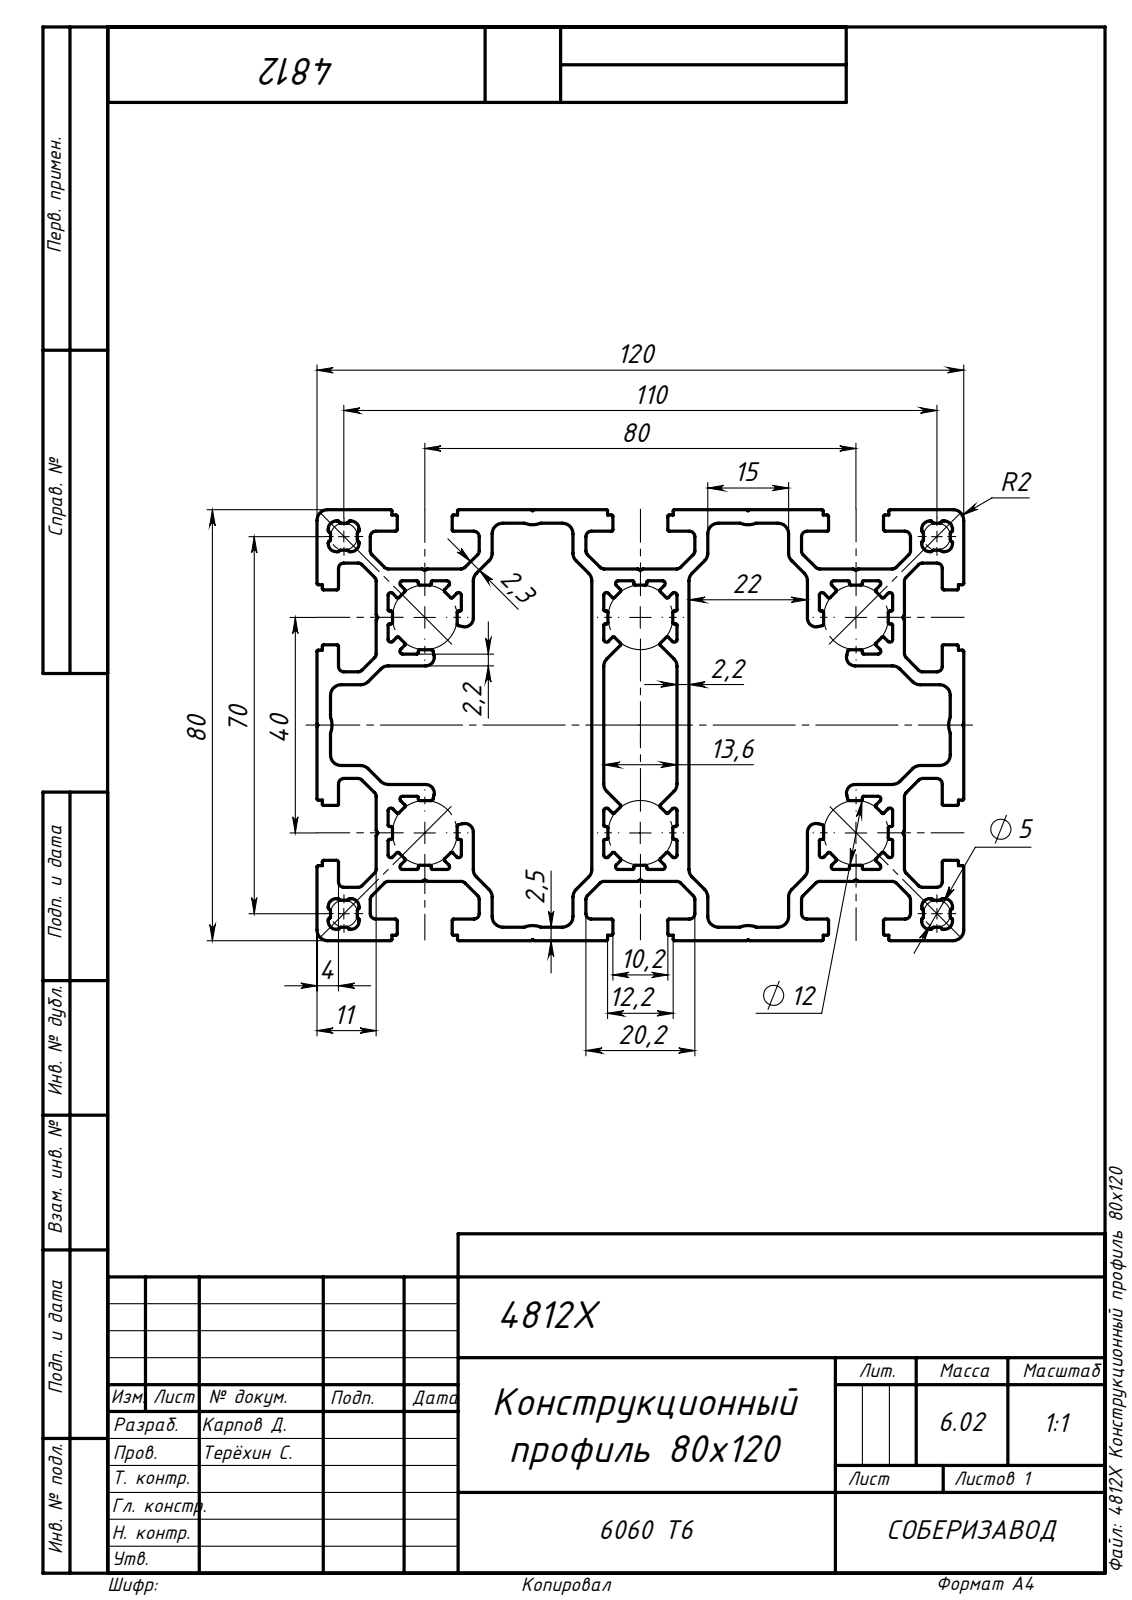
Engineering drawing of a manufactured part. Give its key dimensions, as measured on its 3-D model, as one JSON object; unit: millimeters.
{"part_name": "4812X Конструкционный профиль 80х120", "step_written_by": "SolidWorks 2019 (AUTOMOTIVE_DESIGN)", "units": "millimeters", "bodies": {"solids": 1, "faces": 956, "planar": 514, "cylindrical": 442, "other": 0}, "overall_size": [1000.1, 120, 80], "volume_mm3": 2231000, "surface_area_mm2": 1650000, "partial_cylinders_radius": [[0.25, 248], [1, 60], [2, 44], [0.5, 36], [1.5, 16], [0.3, 8], [0.35, 8], [1.6, 8]], "face_to_face_distances": [69, 40, 2.2, 51, 11, 15.8, 18, 80, 55.8, 66.8]}
